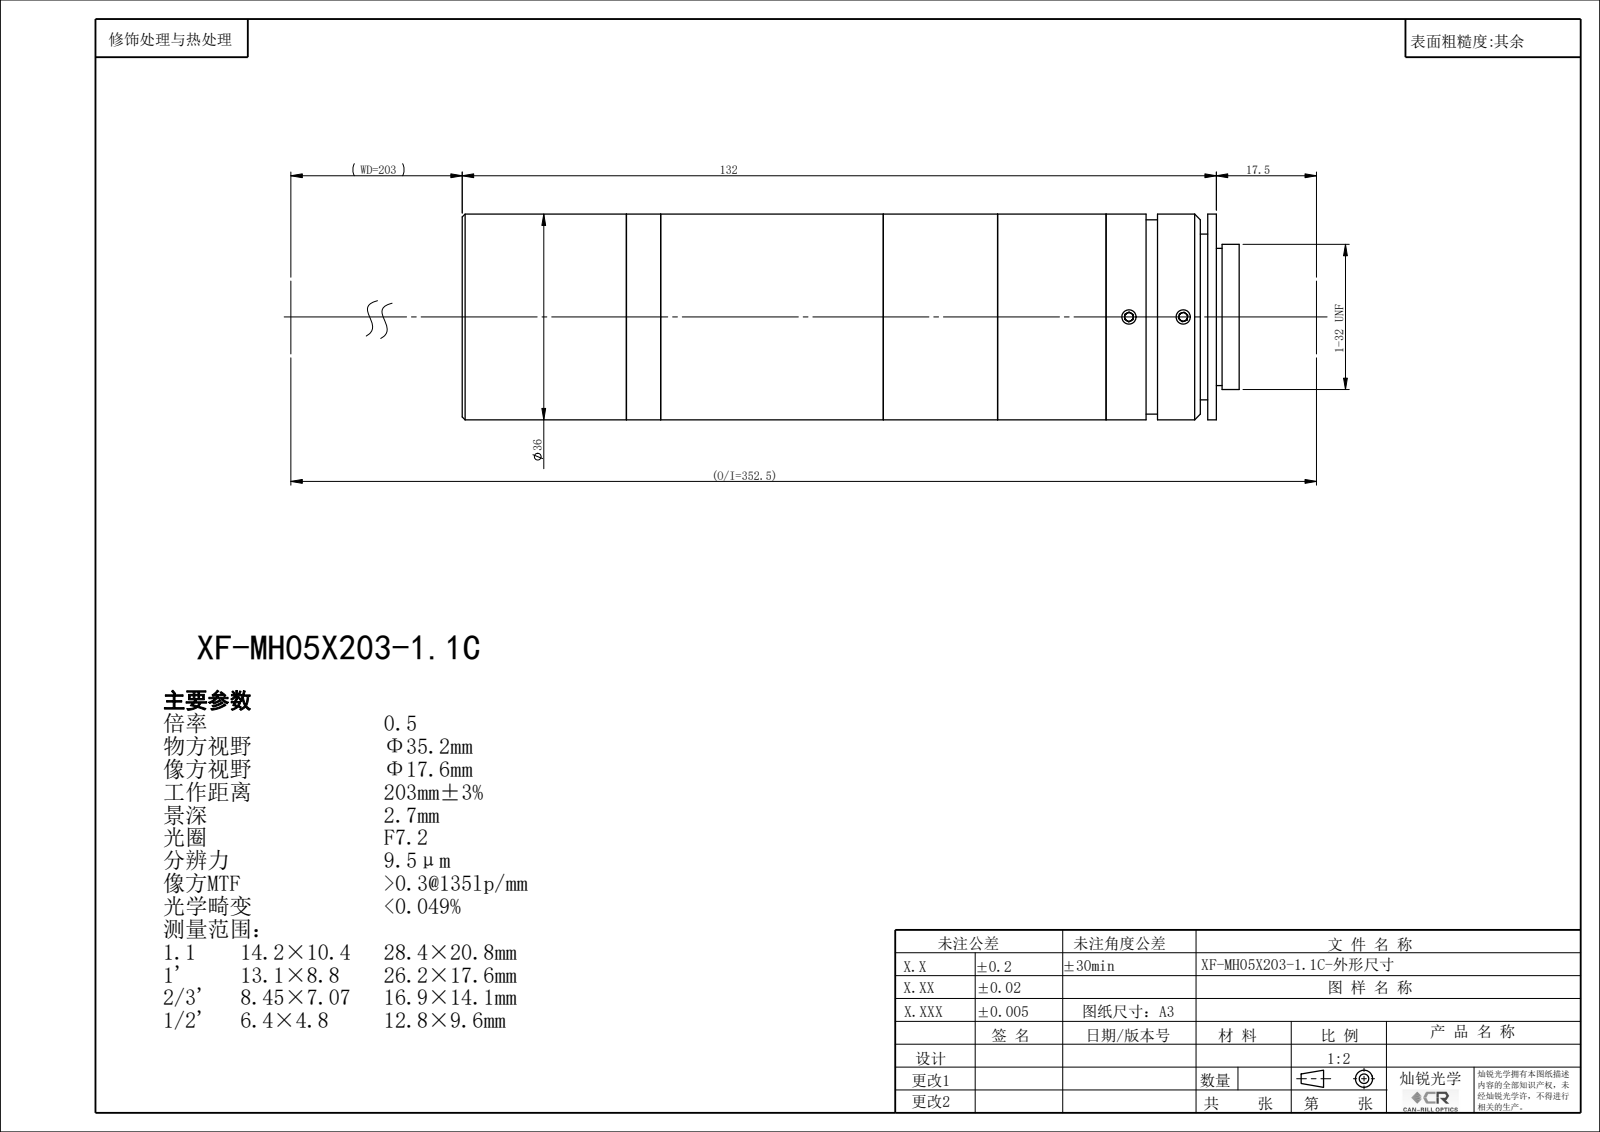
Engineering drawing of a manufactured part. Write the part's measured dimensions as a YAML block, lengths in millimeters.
part_name: "XF-MH05X203-1.1C"
step_written_by: "SolidWorks 2022 (CONFIG_CONTROL_DESIGN)"
units: millimeters
bodies: {solids: 0, faces: 133, planar: 69, cylindrical: 48, other: 16}
overall_size: [136.01, 36, 36]
round_holes:
  - {diameter: 2.5, count: 6}
  - {diameter: 22.4, count: 1}
  - {diameter: 24, count: 1}
  - {diameter: 26, count: 1}
  - {diameter: 26.4, count: 1}
  - {diameter: 29.4, count: 1}
  - {diameter: 33.4, count: 1}
  - {diameter: 34.5, count: 1}
round_bosses_or_shafts:
  - {diameter: 36, count: 1}
  - {diameter: 34, count: 1}
  - {diameter: 25.4, count: 1}
face_to_face_distances: [19.29, 1.5, 17.79, 19, 36.79, 38.29, 20, 39, 56.79, 58.29]
hole_center_spacings: [9.5]
